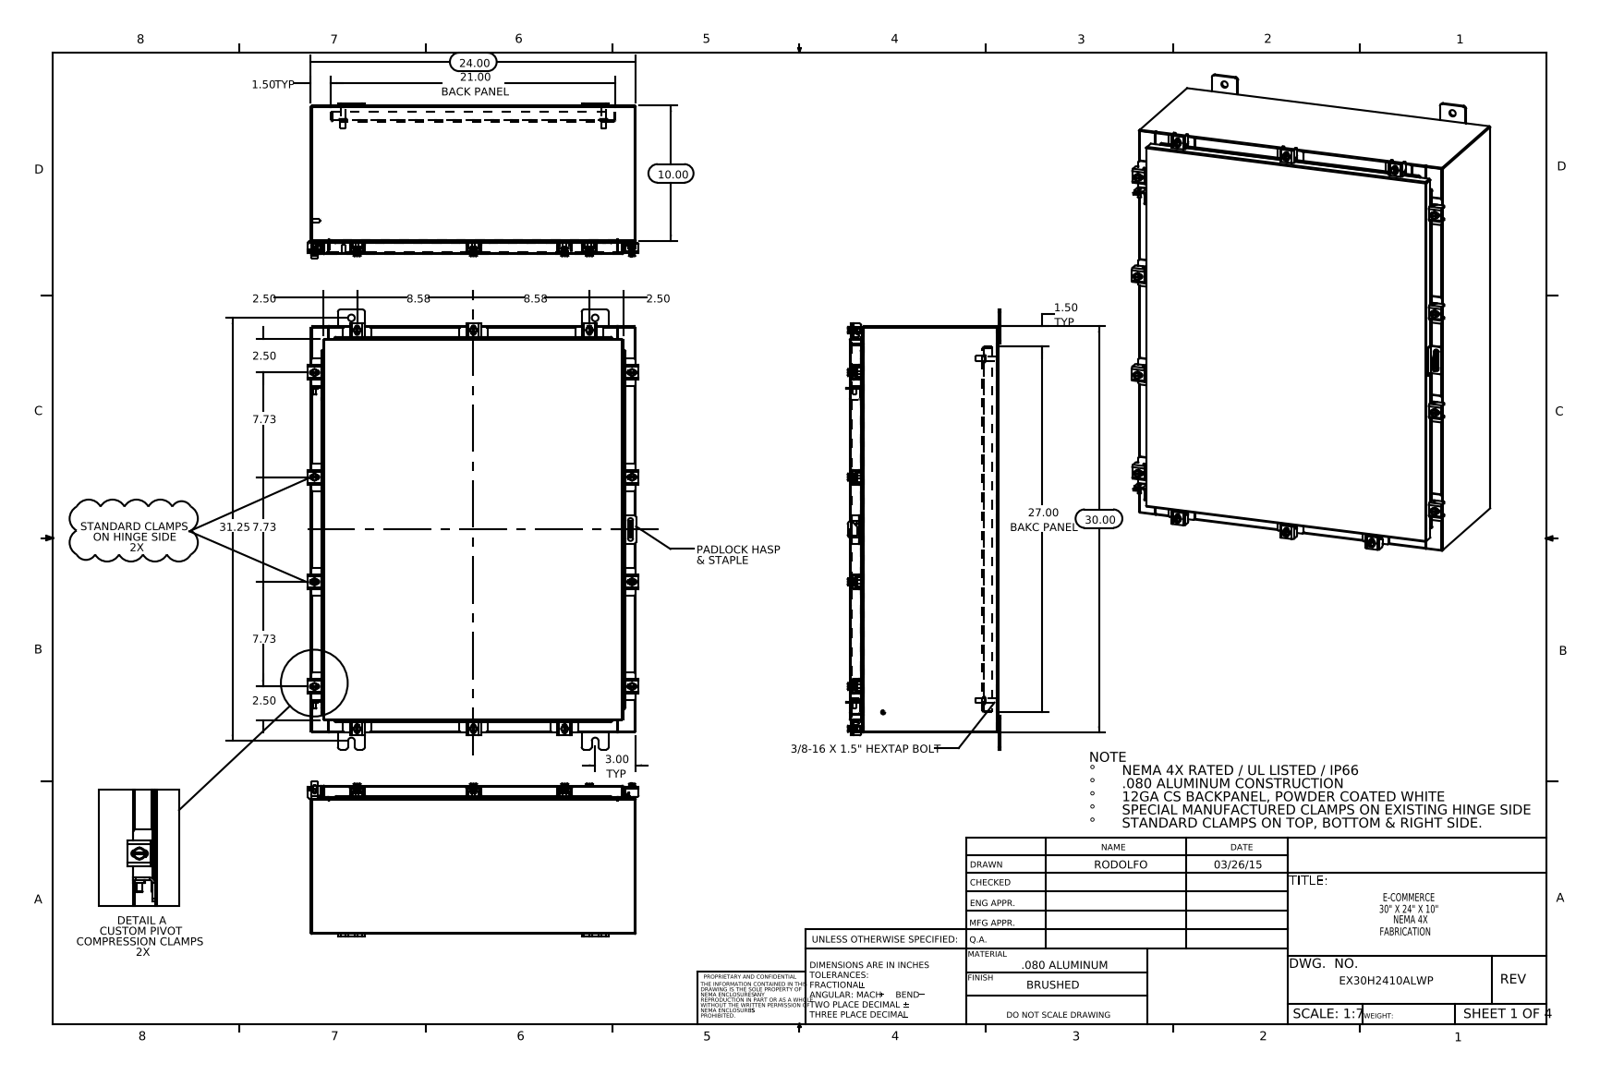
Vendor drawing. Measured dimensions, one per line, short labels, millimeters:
name: EX30H2410ALWP Cover; EX30H2410ALWP Padlock Staple; EX30H2410ALWP Body; 30X10 Clamp Bracket2 (+8 more)
written by: SolidWorks 2014 (CONFIG_CONTROL_DESIGN)
unit: mm
bodies: 91 solids, 2272 faces (1211 planar, 885 cylindrical, 176 other)
size: 825.5 × 620.3 × 290.9
volume: 4 600 000 mm³; area: 4 518 000 mm²
holes: 14× ⌀5.4, 14× ⌀6.6, 8× ⌀12.7, 1× ⌀3.2, 1× ⌀6.4
bosses: 14× ⌀12.7, 14× ⌀6.4, 12× ⌀10.1, 4× ⌀15.9, 4× ⌀9.5, 4× ⌀8.4, 2× ⌀8, 2× ⌀6
rounds: 62× R1.5, 28× R3.6, 26× R0.3, 26× R3, 24× R4.8, 22× R2.2, 22× R2.3, 21× R1.3
face distances: 1.9, 276.9, 278.8, 275, 2.6, 607.7, 25.4, 27.3, 249.6, 251.5
hole spacings: 595.7, 617.5, 820.1, 59.6, 112.8, 521.8, 673.3, 695.2
